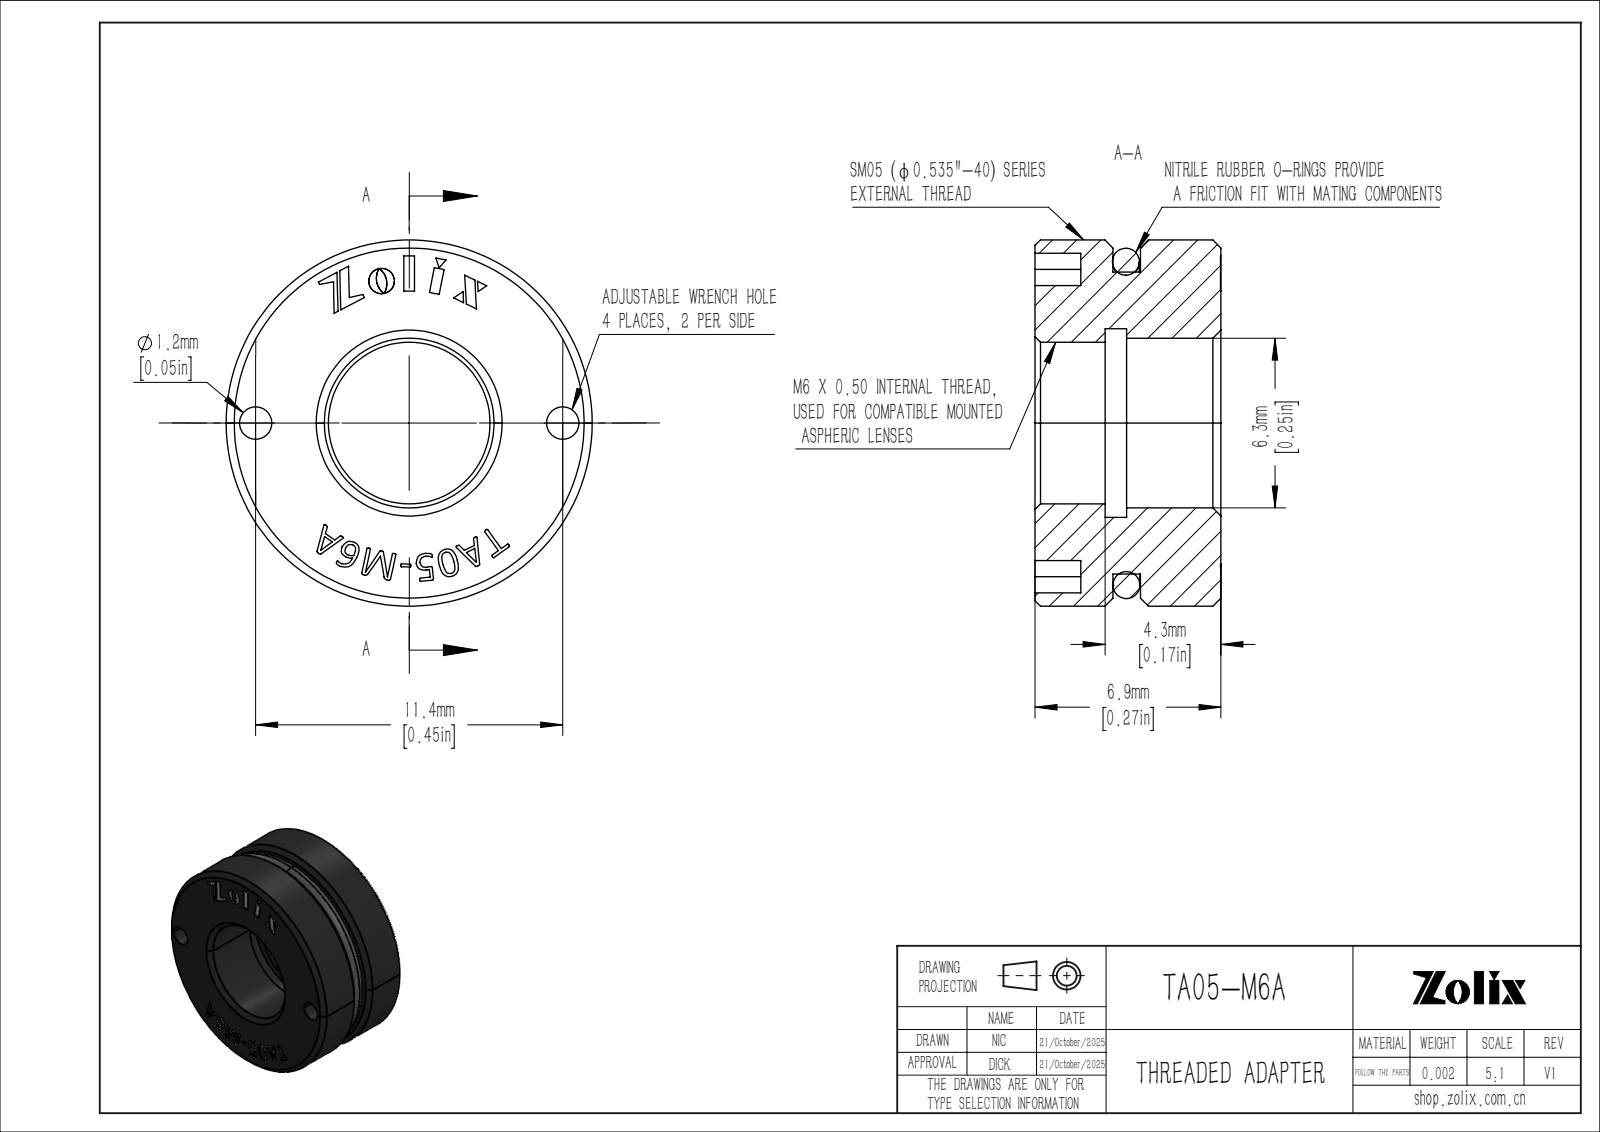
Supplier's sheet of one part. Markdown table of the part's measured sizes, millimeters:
| quantity | value |
| --- | --- |
| part name | TA05-M6A |
| STEP written by | SolidWorks 2020 (CONFIG_CONTROL_DESIGN) |
| units | millimeters |
| bodies | 2 solids, 324 faces (213 planar, 20 cylindrical, 91 other) |
| overall size | 13.59 × 13.59 × 6.9 |
| volume | 754 mm³ |
| surface area | 877 mm² |
| round holes (diameter × count) | 1.2 × 4, 6 × 1, 6.3 × 1, 7 × 1 |
| round bosses / shafts (diameter × count) | 13.59 × 1, 11.2 × 1 |
| main face-to-face distances | 6.9, 2.89, 4.01, 3.91, 1.02, 2.99, 0.51, 2.6, 1.31, 4.3 |
| hole center spacings | 5.7, 8.06, 11.4 |
